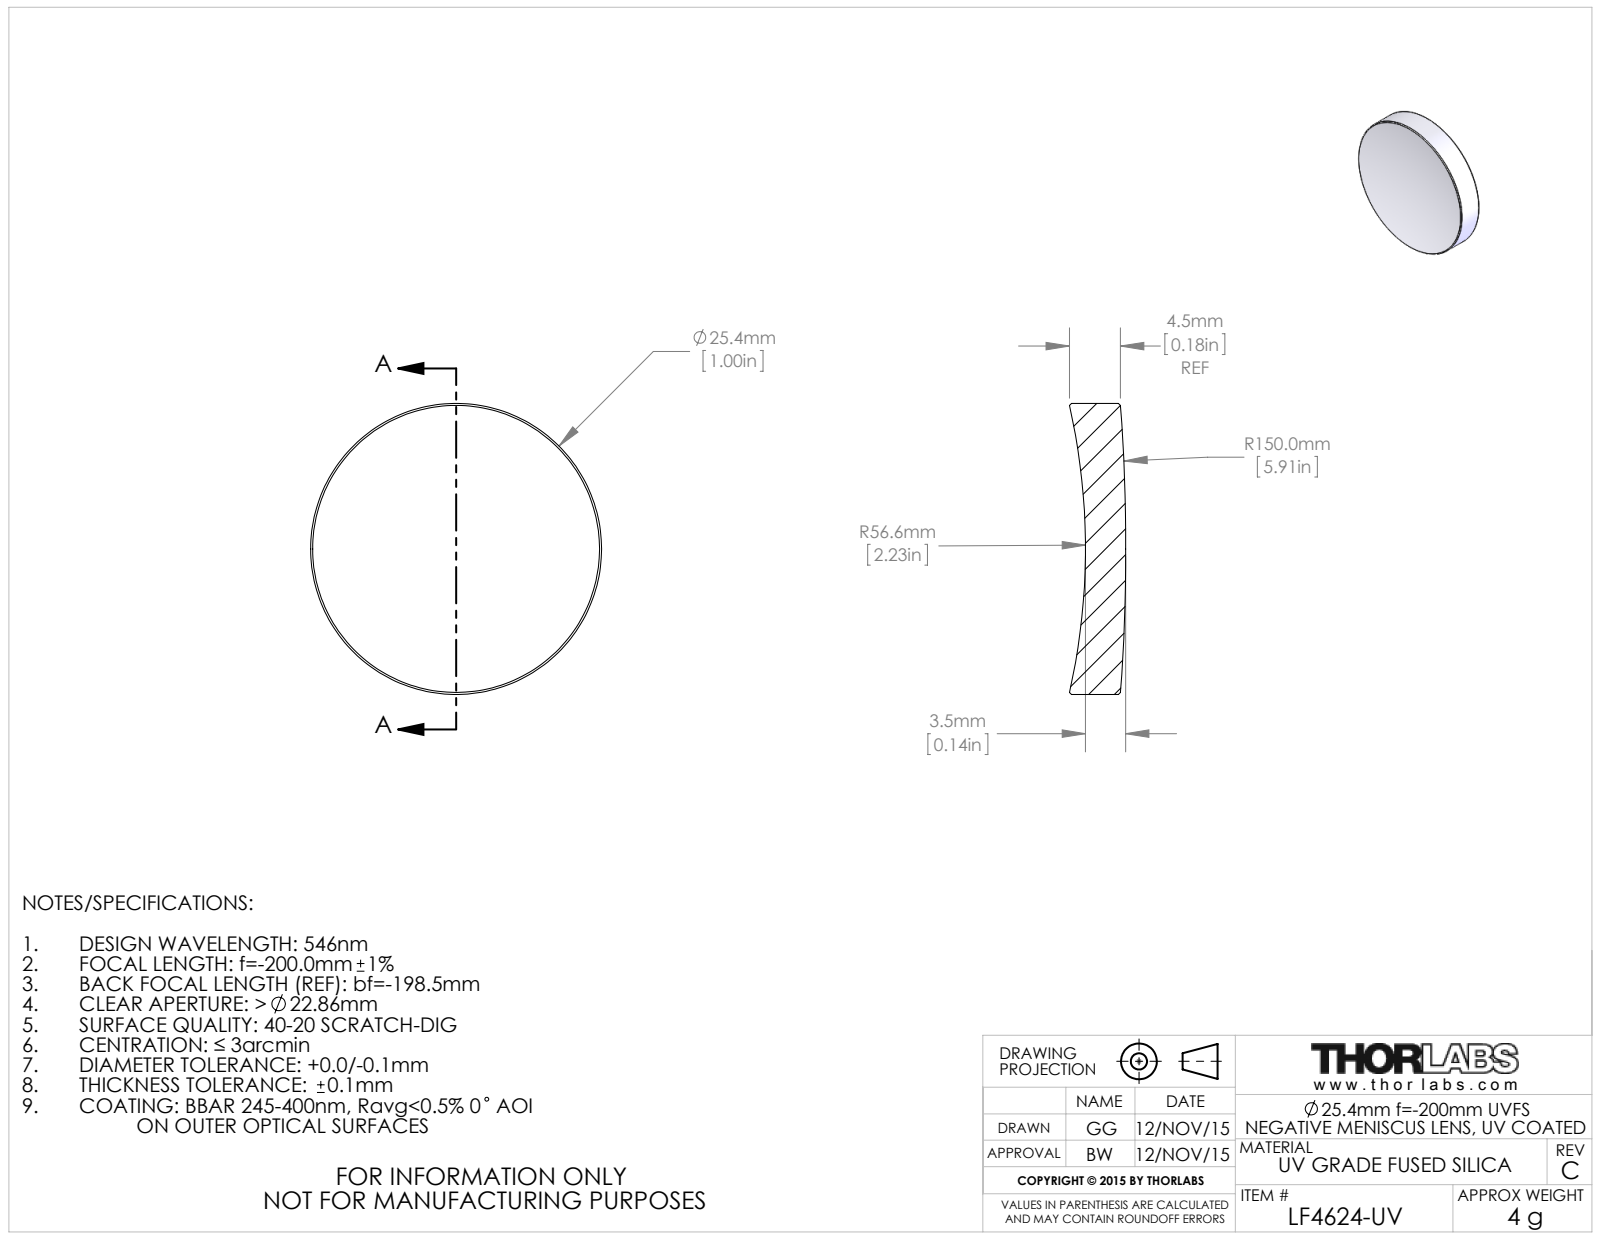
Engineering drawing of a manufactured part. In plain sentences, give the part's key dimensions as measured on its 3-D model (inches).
The part is named "4939-E0W". Its 3-D file was written by "SolidWorks 2014 (CONFIG_CONTROL_DESIGN)". It is 1 solid with 10 faces: 0 planar, 2 cylindrical and 8 other. Overall it measures 1 by 1 by 0.193 inches. Its volume is 0.124 cubic inches and its surface area 2.107 square inches. Round bosses or shafts: 1 of diameter 1.
